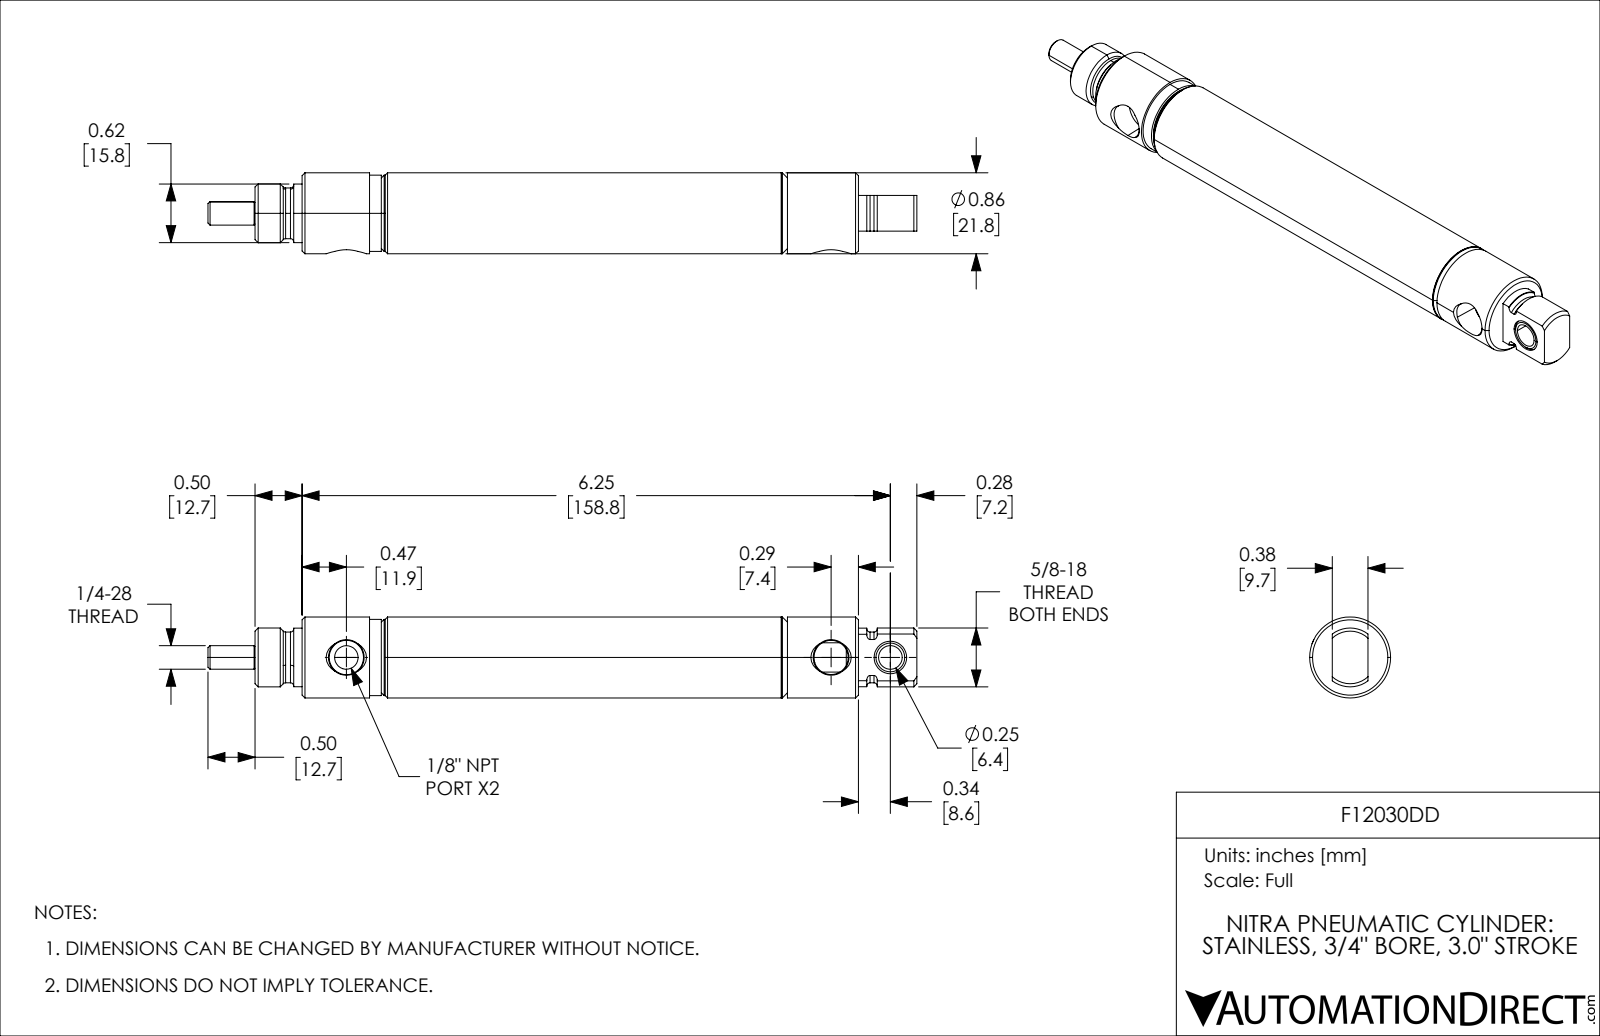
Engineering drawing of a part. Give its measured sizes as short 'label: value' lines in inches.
name: F12030DD_7; F12030DD_3; F12030DD_11; F12030DD (+2 more)
written by: SolidWorks 2021 (CONFIG_CONTROL_DESIGN)
unit: in
bodies: 5 solids, 158 faces (29 planar, 61 cylindrical, 68 other)
size: 7.532 × 0.86 × 0.86
volume: 2.309 in³; area: 43.12 in²
holes: 1× ⌀0.25, 1× ⌀0.251, 1× ⌀0.274, 1× ⌀0.312, 1× ⌀0.346, 1× ⌀0.363, 1× ⌀0.5, 1× ⌀0.702
bosses: 1× ⌀0.86, 1× ⌀0.81, 1× ⌀0.762, 1× ⌀0.625, 1× ⌀0.622, 1× ⌀0.539, 1× ⌀0.25, 1× ⌀0.23
rounds: 1× R0.269
face distances: 0.844, 1.594, 5.438, 3, 3.844, 4.816, 1.816, 0.972, 0.5, 0.38
hole spacings: 0.63, 5.15, 5.78
